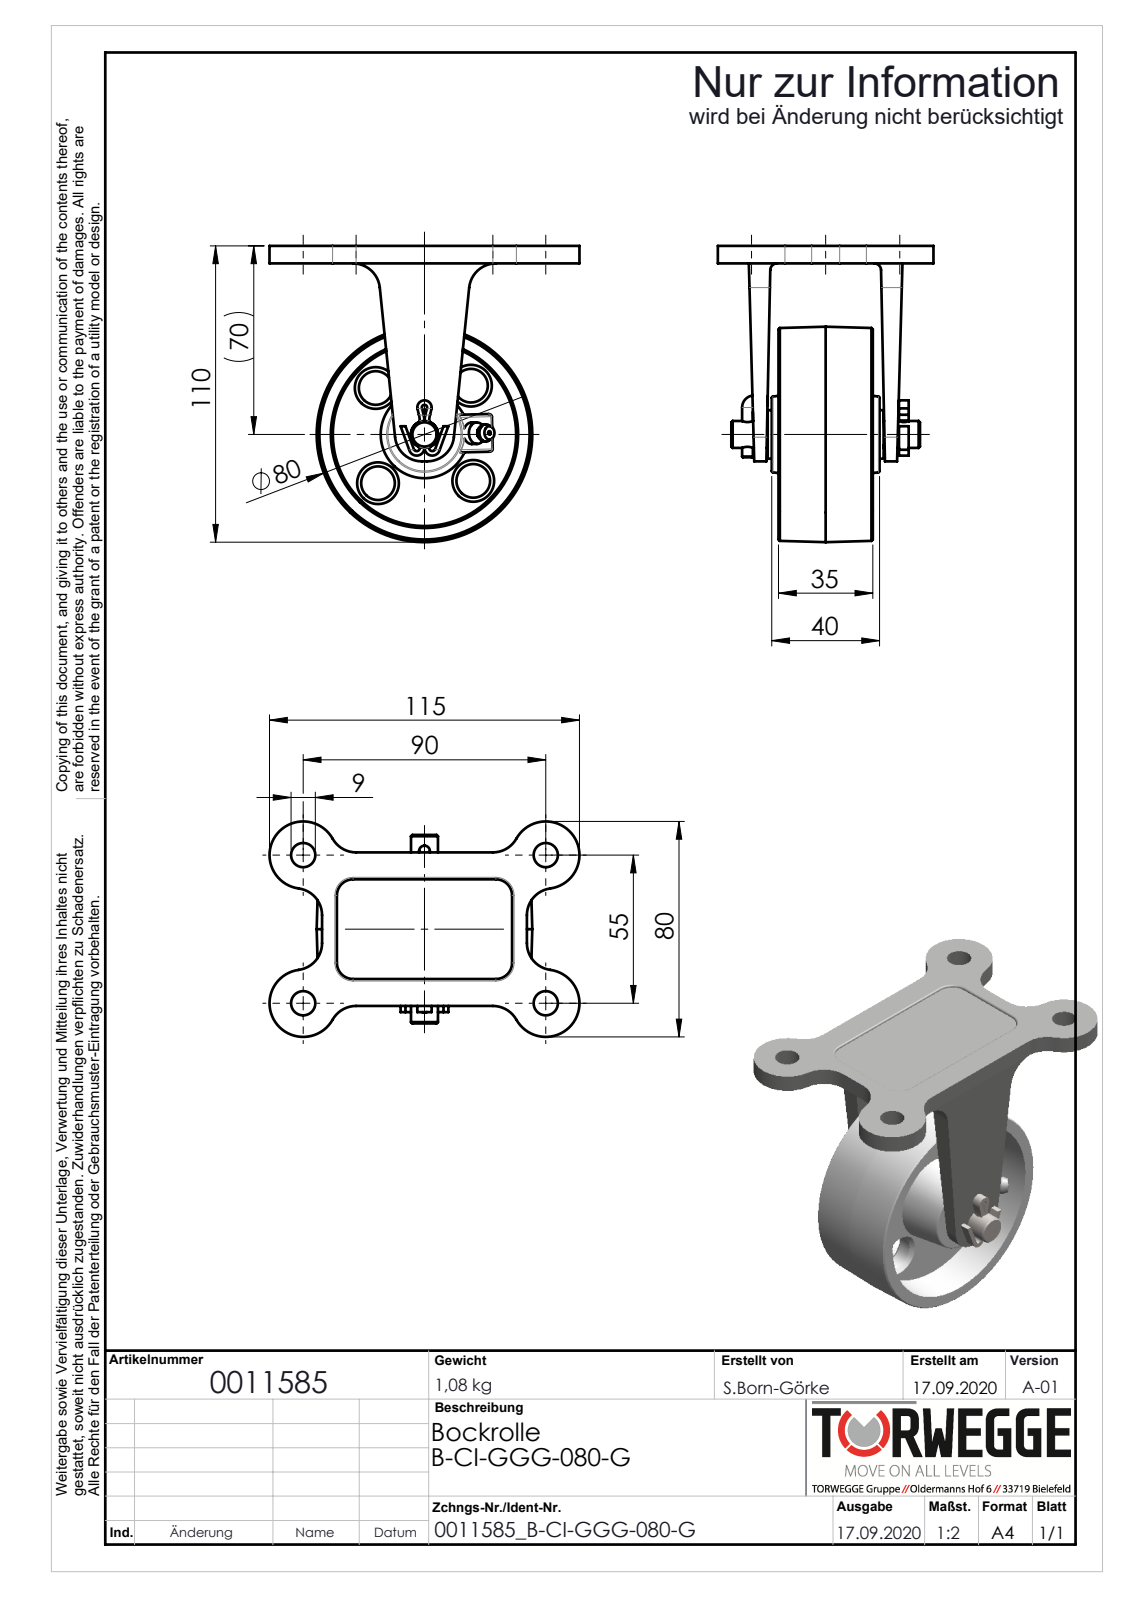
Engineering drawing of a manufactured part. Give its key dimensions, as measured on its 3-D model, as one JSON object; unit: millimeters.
{"part_name": "0011585", "step_written_by": "SolidWorks 2018 (AUTOMOTIVE_DESIGN)", "units": "millimeters", "bodies": {"solids": 9, "faces": 257, "planar": 77, "cylindrical": 102, "other": 78}, "overall_size": [115, 110, 80], "volume_mm3": 158805, "surface_area_mm2": 61238, "round_holes": [[9, 4], [12.5, 4], [4, 2], [6, 1], [10.1, 1], [10.2, 1], [10.5, 1], [12, 1]], "round_bosses_or_shafts": [[18, 1], [10, 1], [8, 1], [6, 1], [4, 1]], "partial_cylinders_radius": [[10, 12], [0.75, 4], [12.5, 4], [0.5, 3], [1, 2], [1.2, 2], [2.5, 2], [2.86, 2]], "face_to_face_distances": [6.5, 5.75, 0.75, 13.5, 8, 21.5, 2.5, 16, 24, 37.5], "hole_center_spacings": [25, 35.35, 45.02, 72.23, 49.99, 55, 90, 105.48]}
